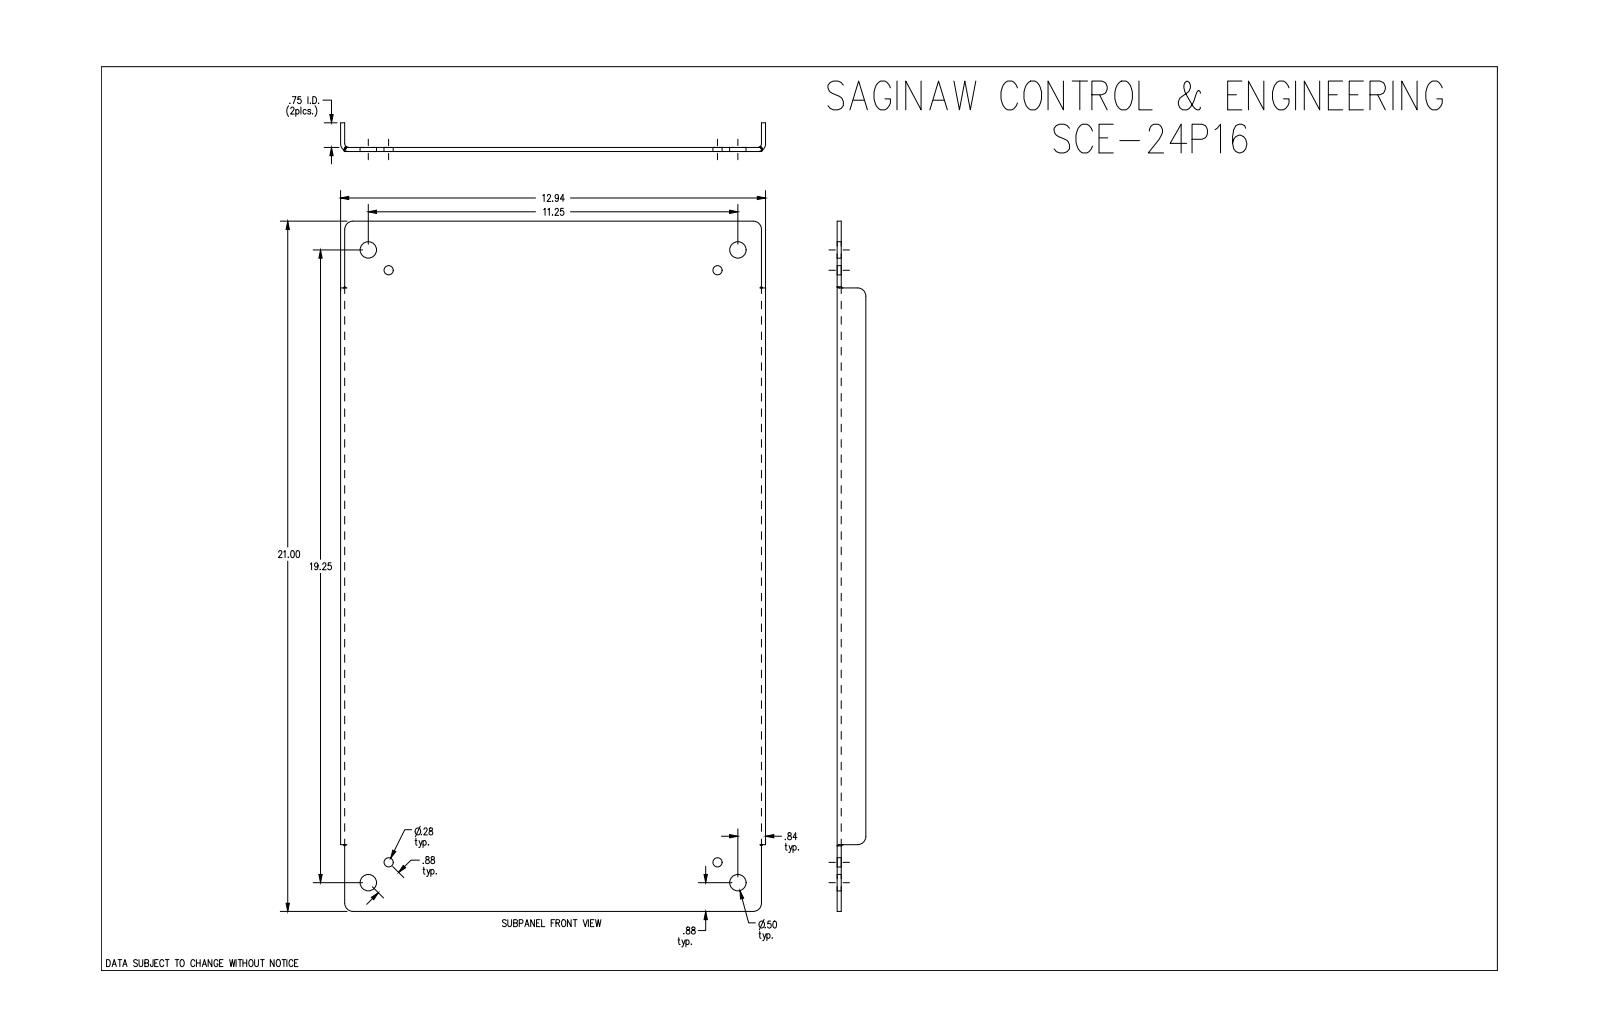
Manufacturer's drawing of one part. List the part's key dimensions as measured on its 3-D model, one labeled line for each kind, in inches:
Part name (STEP PRODUCT): SCE-24P16
STEP written by: SolidWorks 2019 (CONFIG_CONTROL_DESIGN)
Units: inches
Bodies: 1 solid, 50 faces (18 planar, 20 cylindrical, 12 other)
Overall size (bounding box): 21 × 12.938 × 0.875
Volume: 36.55 in³ · Surface area: 594.7 in²
Round holes (diameter × count): ⌀0.281 ×4, ⌀0.5 ×4
Partial cylindrical surfaces — rounded edges, fillets, slot ends (radius × count): R0.25 ×6, R0.112 ×2, R0.237 ×2
Main face-to-face distances: 0.125, 0.125, 12.813, 12.687, 12.938, 0.75, 0.875, 21, 2.031, 18.969
Hole centre spacings: 0.875, 10.65, 18.641, 21.451, 10.013, 11.25, 18.013, 19.25
